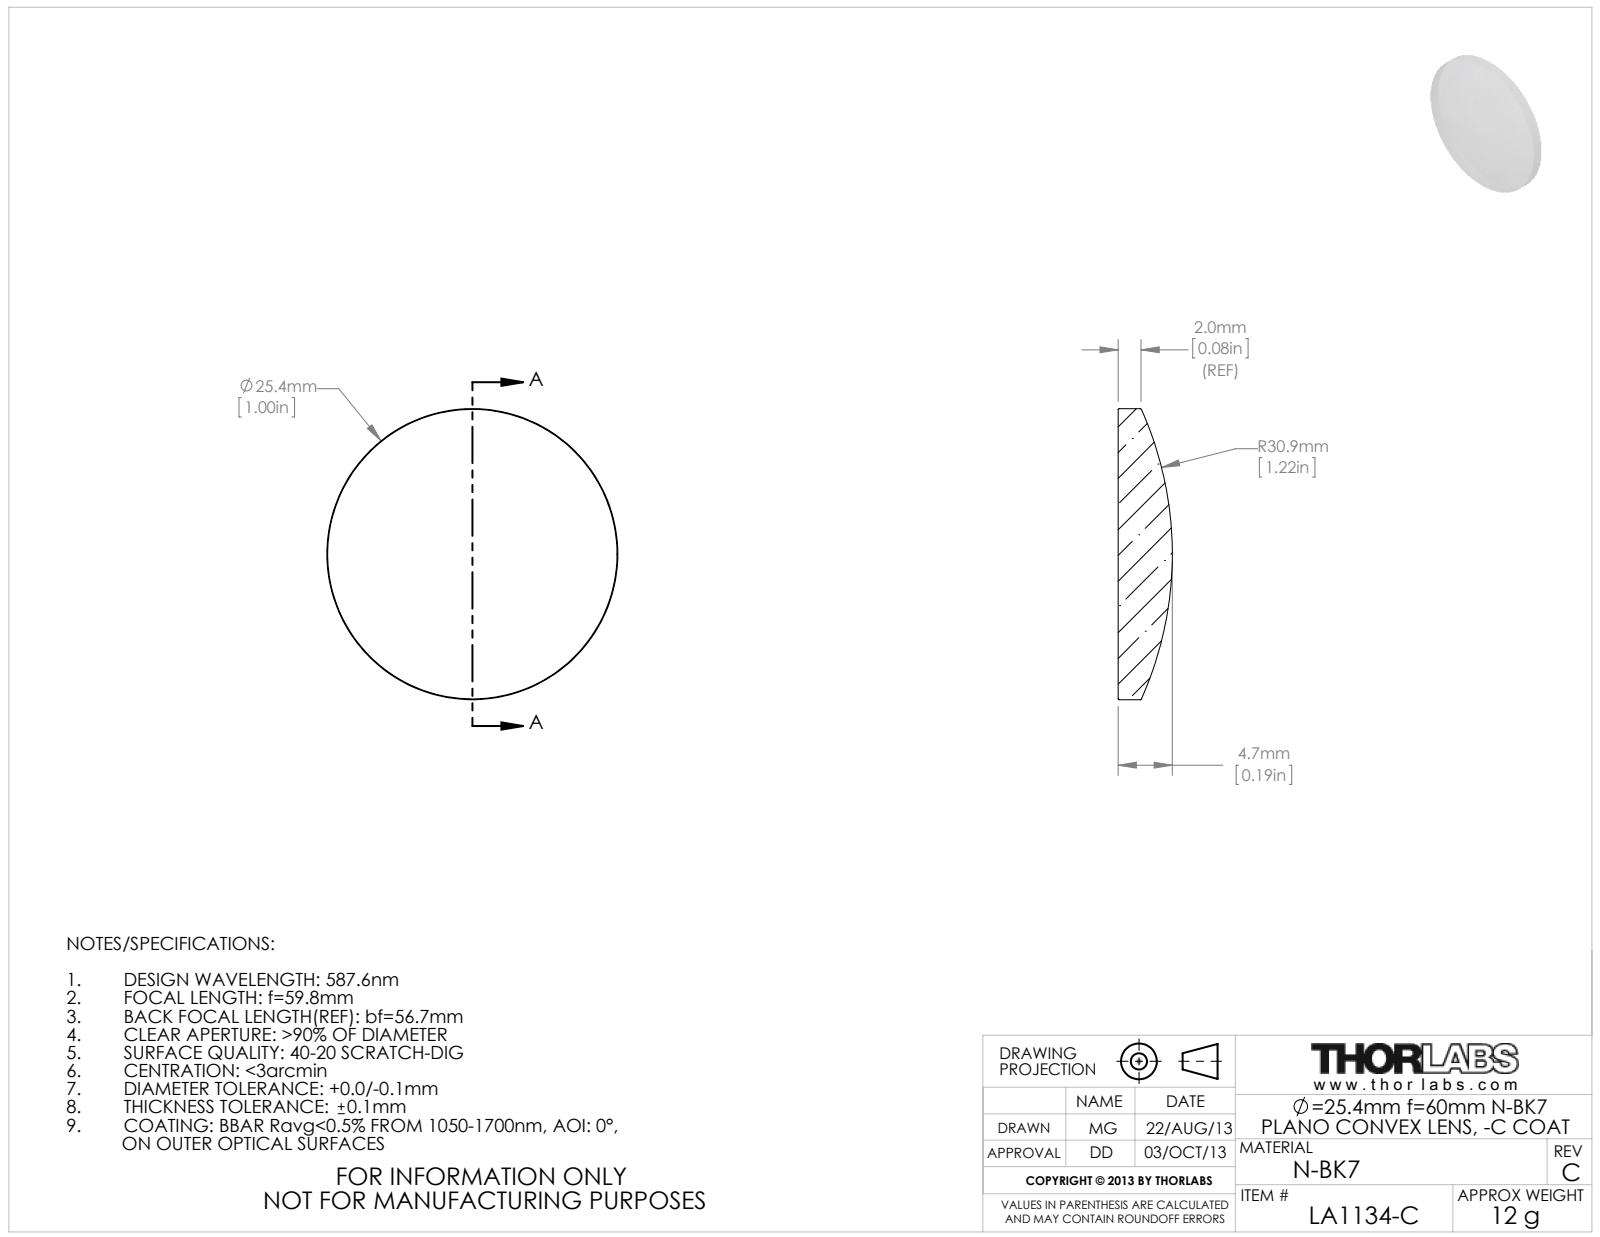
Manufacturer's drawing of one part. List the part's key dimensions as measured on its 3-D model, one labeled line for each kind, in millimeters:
Part name (STEP PRODUCT): 4582-E0W
STEP written by: SolidWorks 2009 (AUTOMOTIVE_DESIGN)
Units: millimetres
Bodies: 1 solid, 5 faces (1 planar, 2 cylindrical, 2 other)
Overall size (bounding box): 25.4 × 25.4 × 4.73
Volume: 1 716 mm³ · Surface area: 1 196 mm²
Round bosses / shafts (diameter × count): ⌀25.4 ×1
